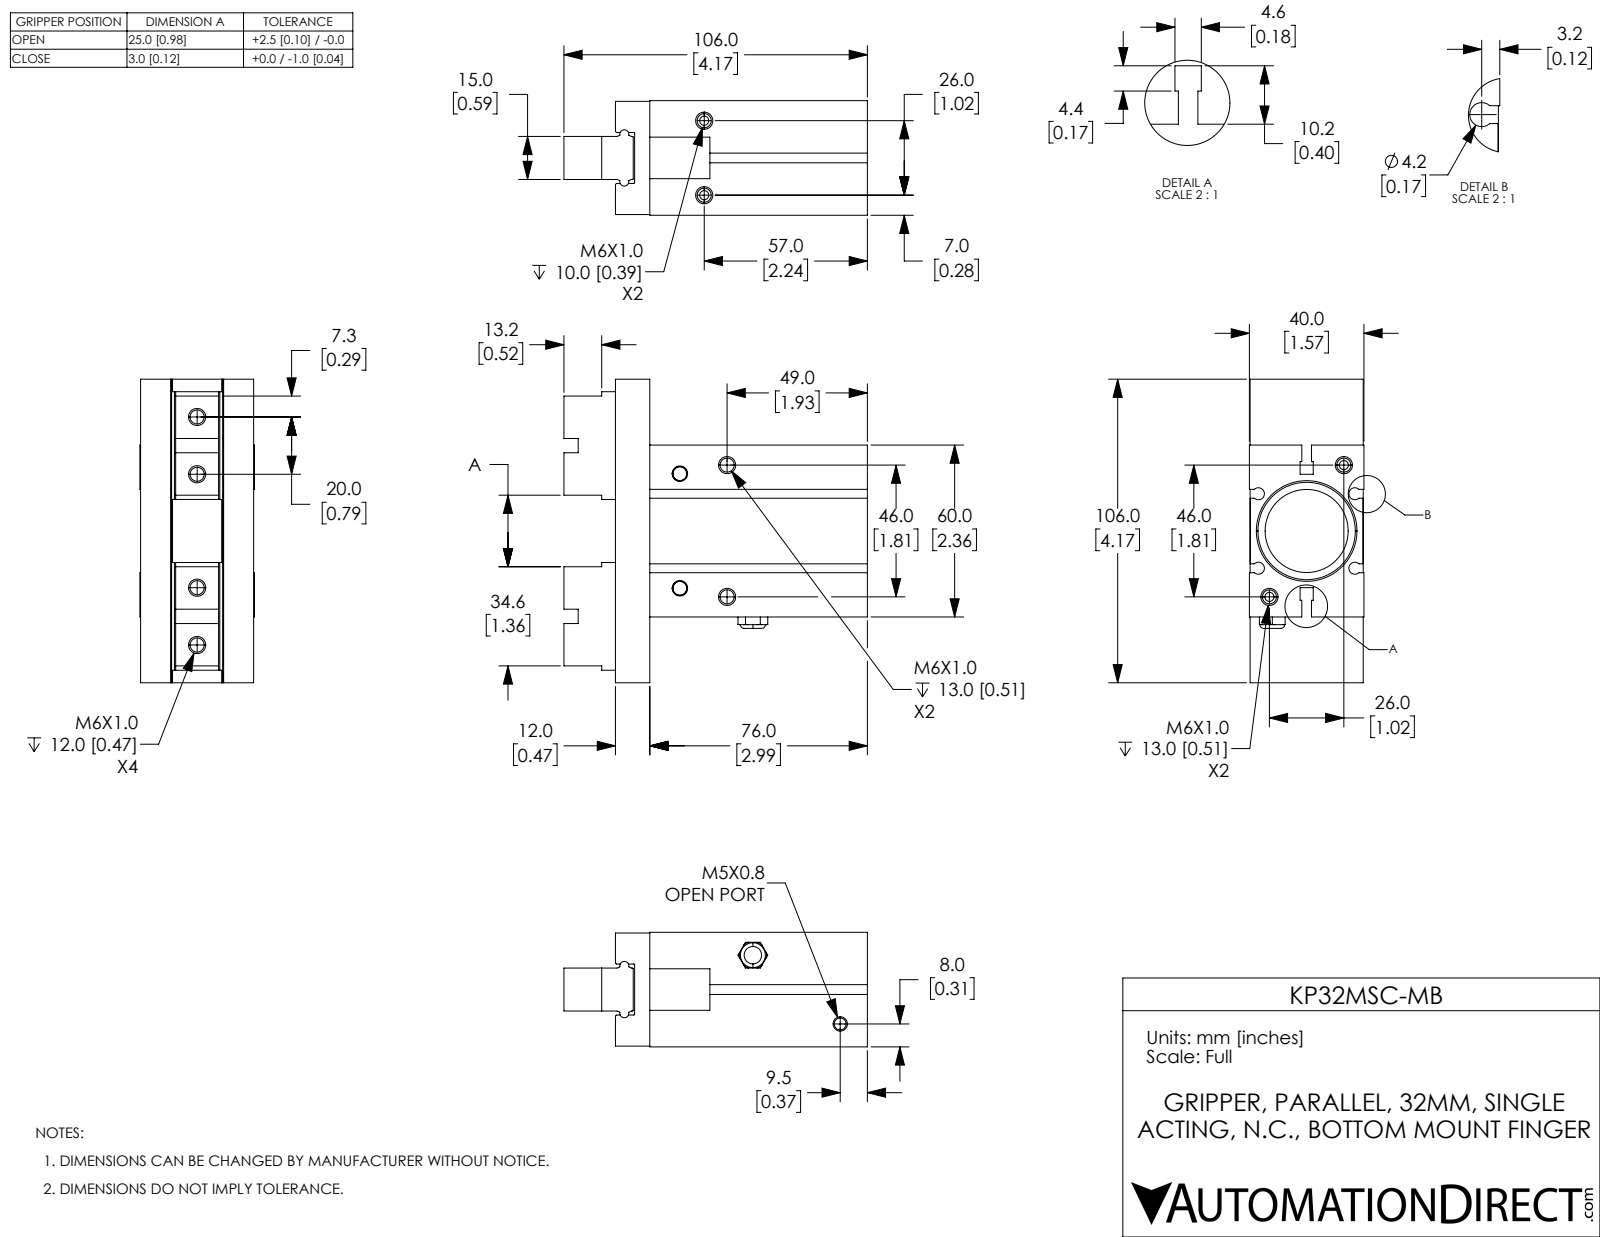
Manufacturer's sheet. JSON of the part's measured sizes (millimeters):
{"part_name": "KP32MSC-MB-1; KP32MSC-MB-3; KP32MSC-MB-2; KP32MSC-MB", "step_written_by": "SolidWorks 2017 (CONFIG_CONTROL_DESIGN)", "units": "millimeters", "bodies": {"solids": 3, "faces": 261, "planar": 135, "cylindrical": 64, "other": 62}, "overall_size": [106, 106, 40], "volume_mm3": 209878, "surface_area_mm2": 48358, "round_holes": [[4.92, 4], [0.5, 2], [4.13, 2], [4.92, 2], [6.02, 2], [6.1, 1], [29, 1], [34, 1]], "partial_cylinders_radius": [[0.2, 6], [2.1, 4], [2.46, 4], [2.46, 4], [0.3, 2], [1.59, 2]], "face_to_face_distances": [12.5, 27.25, 39.7, 27.5, 12.2, 27.2, 12.75, 39.75, 12.25, 39.45], "hole_center_spacings": [26.42, 17.03, 26, 30.23, 38.81, 46, 47.51, 52.84]}
